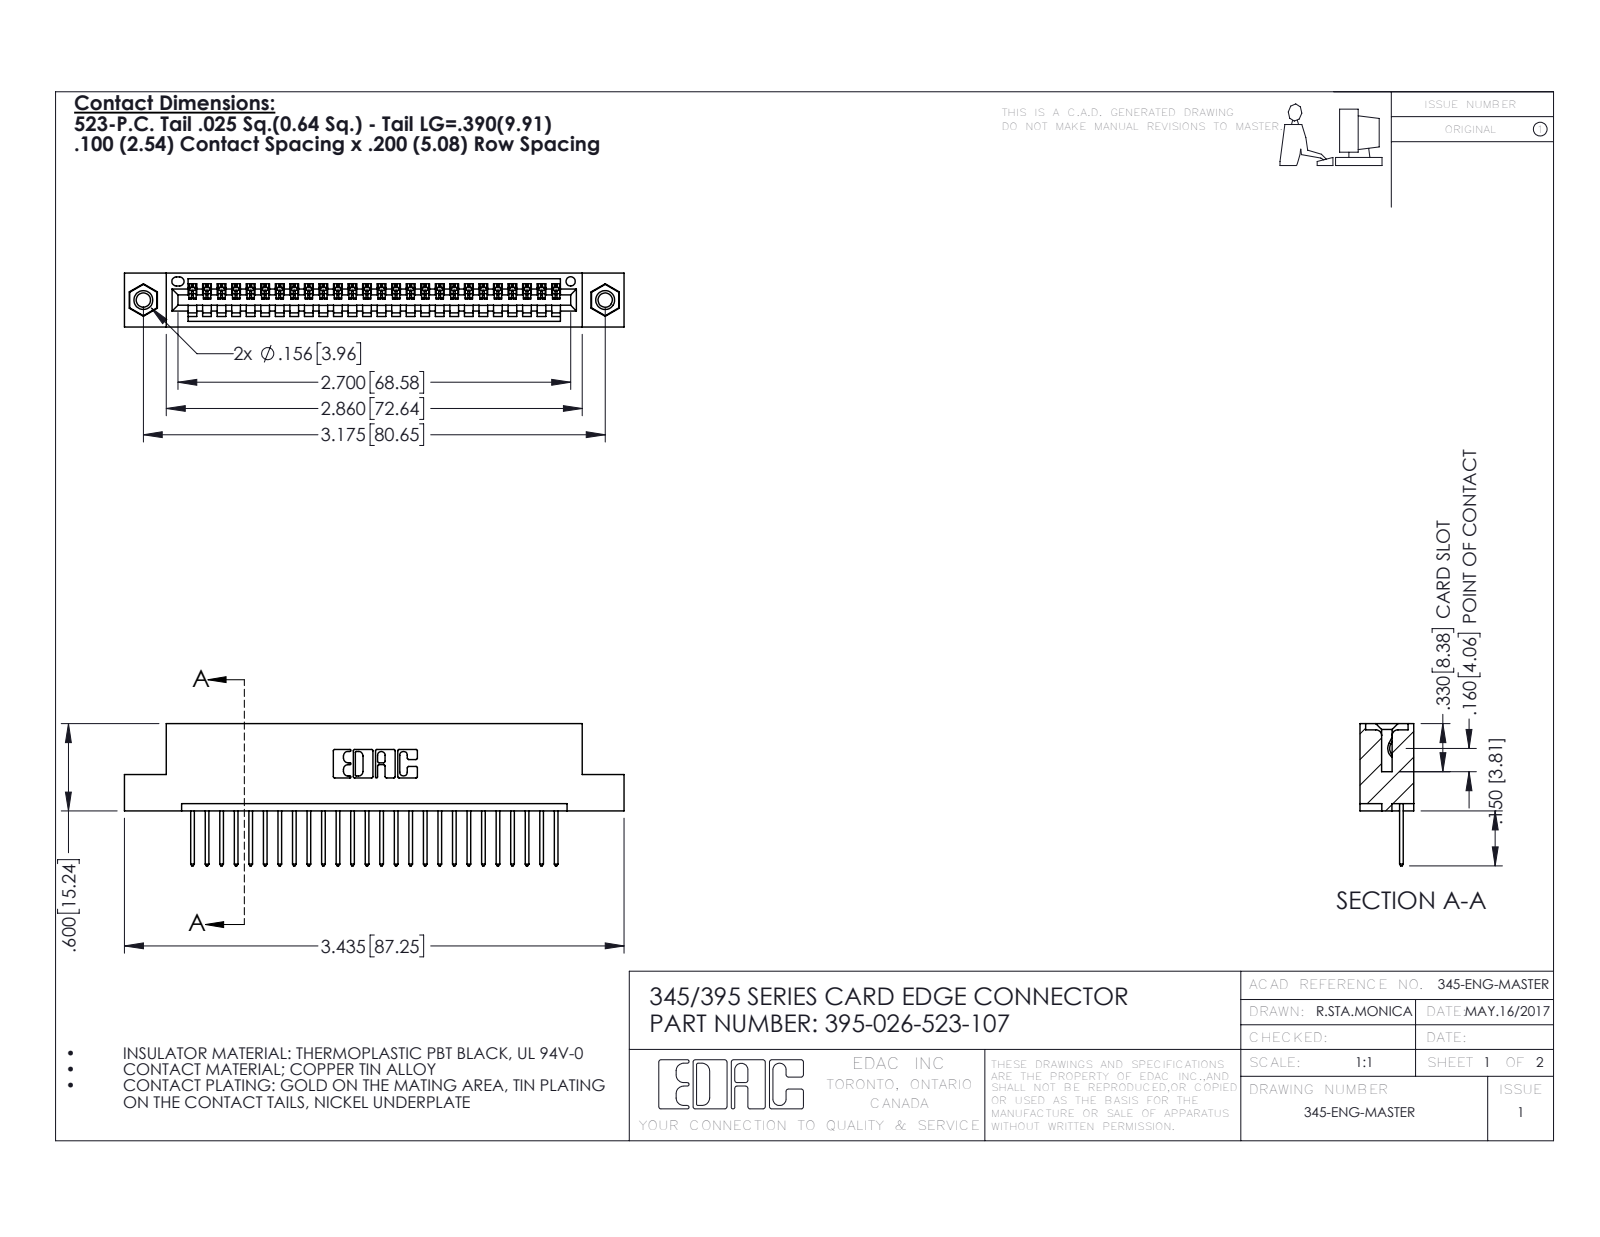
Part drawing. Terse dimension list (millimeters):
name: 345-250-001_345-250-005-103; 345-292-001_345-293-123; 395-026-523-107; 345 Part_Flush Mounting Lugs - 0.156 Dia-TI
written by: SolidWorks 2016 (CONFIG_CONTROL_DESIGN)
unit: mm
bodies: 29 solids, 1694 faces (1152 planar, 526 cylindrical, 16 other)
size: 87.2 × 24.8 × 9.4
volume: 8 130 mm³; area: 10 650 mm²
holes: 2× ⌀2.5, 2× ⌀3.2, 2× ⌀4, 1× ⌀1.6
bosses: 2× ⌀3.9
rounds: 52× R0.2, 52× R0.3, 22× R0.3, 6× R0.2, 6× R0.8, 3× R0.7, 2× R0.8, 2× R1
face distances: 1.8, 7.6, 5.1, 9.4, 2.5, 6.9, 0.6, 5.7, 3.8, 1.8
hole spacings: 6.9, 74.7, 80.6
